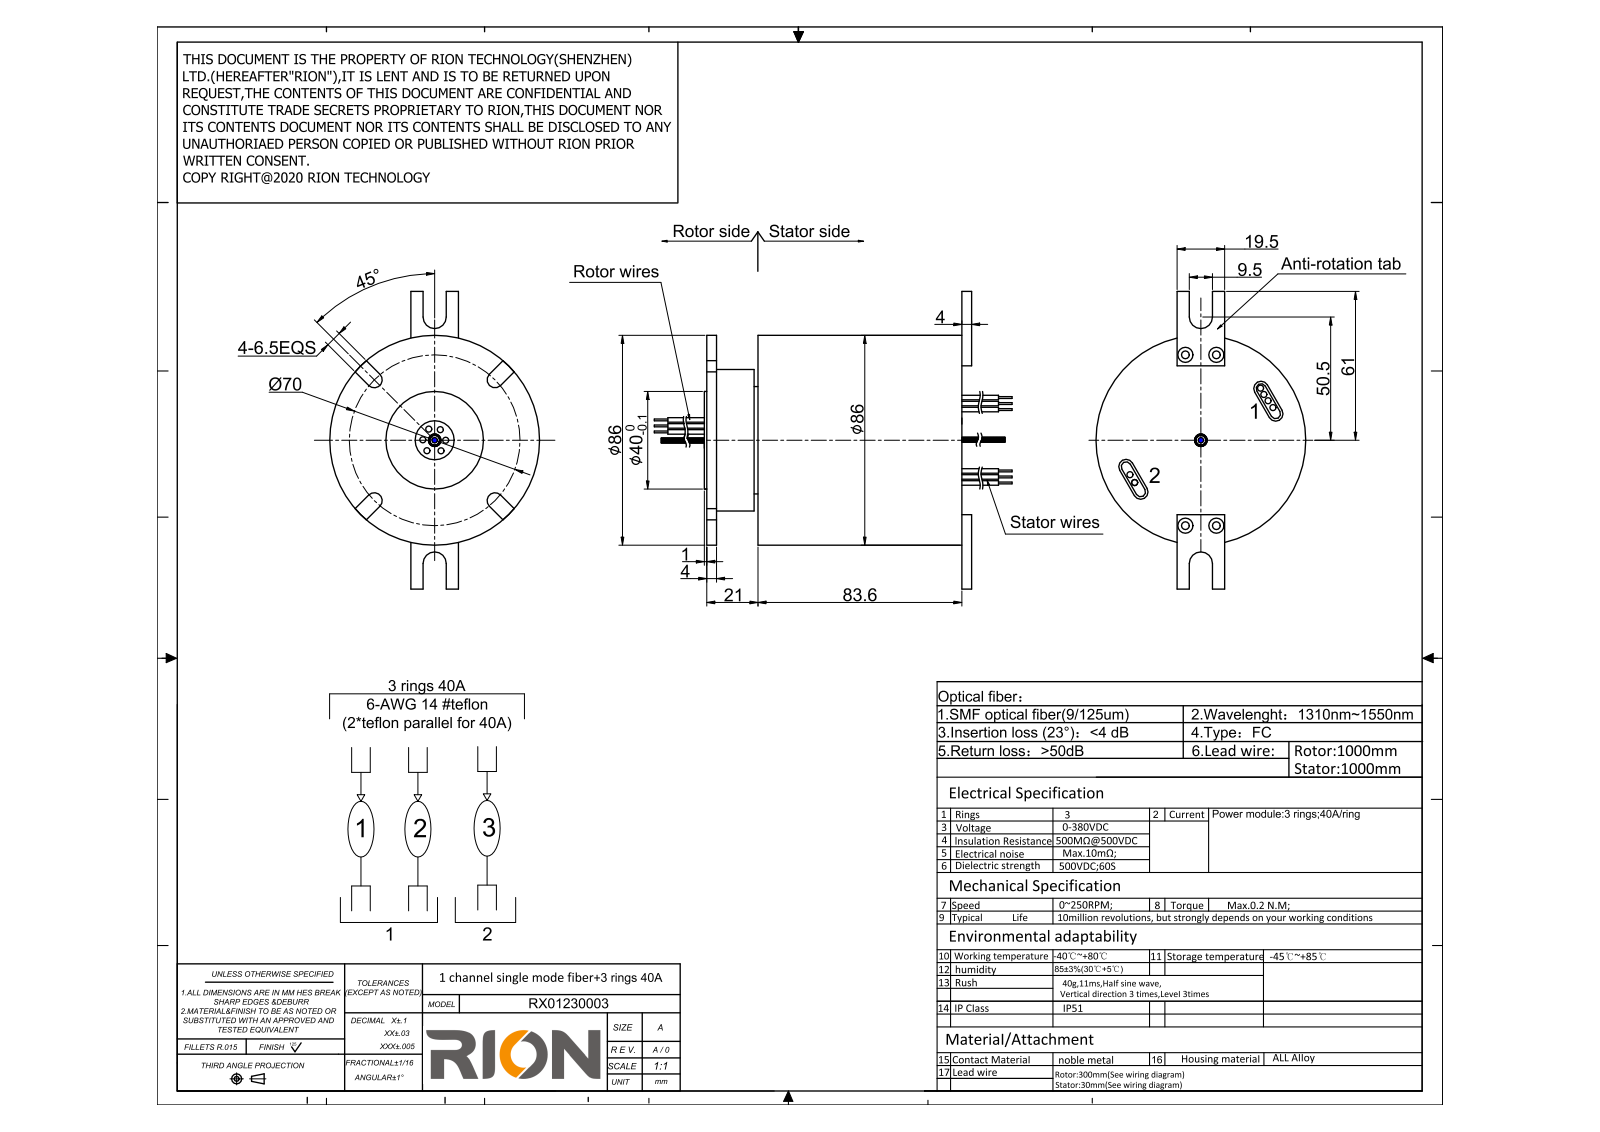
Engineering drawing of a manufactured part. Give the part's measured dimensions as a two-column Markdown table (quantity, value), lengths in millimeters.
| quantity | value |
| --- | --- |
| STEP written by | SolidWorks 2014 (CONFIG_CONTROL_DESIGN) |
| units | millimeters |
| bodies | 1 solid, 155 faces (58 planar, 81 cylindrical, 16 other) |
| overall size | 144.6 × 122 × 86 |
| volume | 560 793 mm³ |
| surface area | 54 280 mm² |
| round holes (diameter × count) | 2.5 × 4, 3.2 × 4, 20 × 1, 82 × 1 |
| round bosses / shafts (diameter × count) | 2.5 × 12, 86 × 1, 81.8 × 1, 60 × 1, 44 × 1, 40 × 1, 5.2 × 1 |
| partial cylindrical surfaces (radius × count) | 3.25 × 4, 3.25 × 4, 4.75 × 2, 27.75 × 1, 34.26 × 1 |
| main face-to-face distances | 21, 104.6, 83.6, 4, 100.6, 17, 1, 20, 16, 84.6 |
| hole center spacings | 35.57, 12.7, 70, 71.14 |
